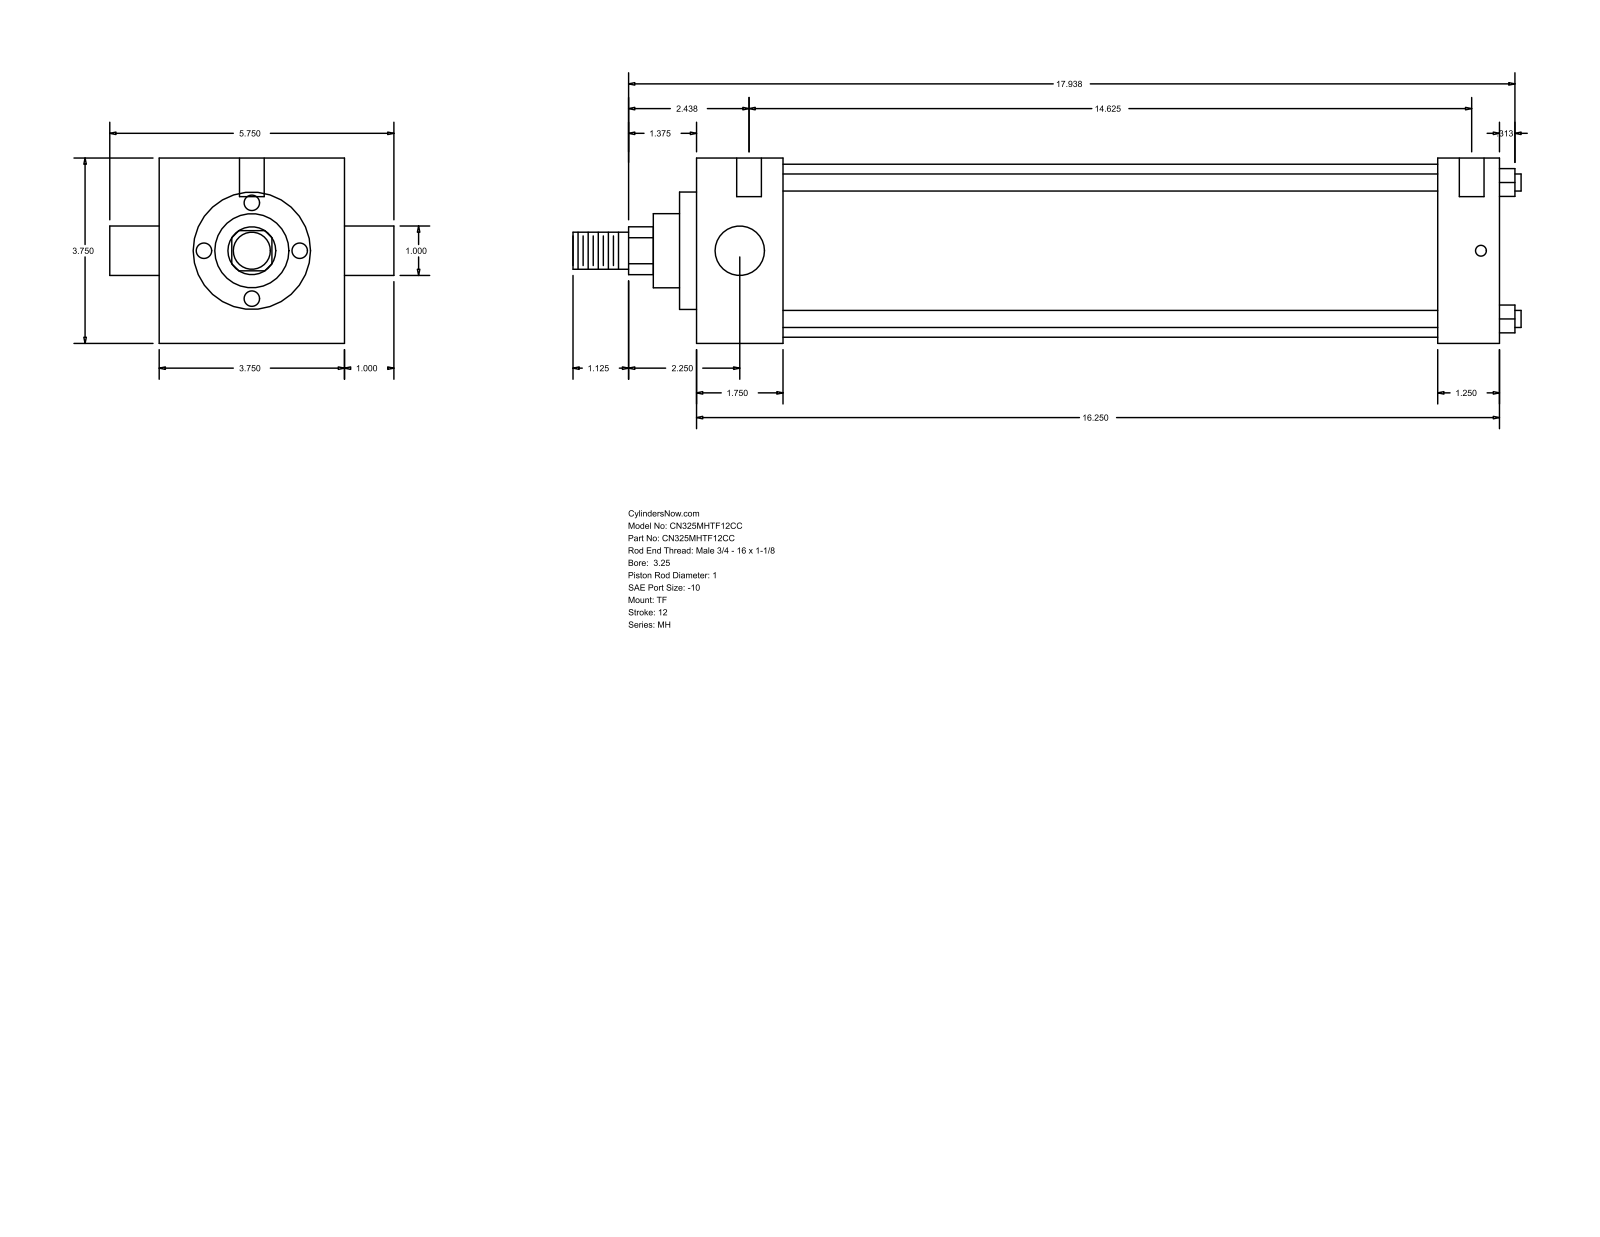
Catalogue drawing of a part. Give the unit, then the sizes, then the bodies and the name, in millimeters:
Units: millimetres
Overall size (bounding box): 487.36 × 146.05 × 95.25
Round holes (diameter × count): ⌀5.56 ×3, ⌀12.7 ×2
Round bosses / shafts (diameter × count): ⌀8.76 ×4, ⌀25.4 ×2, ⌀88.9 ×1, ⌀60.33 ×1, ⌀38.1 ×1, ⌀19.05 ×1
Partial cylindrical surfaces — rounded edges, fillets, slot ends (radius × count): R12.29 ×1
Main face-to-face distances: 95.24, 412.76, 44.46, 381.01, 336.55, 368.3, 31.75, 8.73, 53.19, 389.74
Hole centre spacings: 1.58, 4.76, 371.48, 373.06, 376.24, 377.82
Bodies: 0 solids, 86 faces (61 planar, 25 cylindrical, 0 other)
Part name (STEP PRODUCT): MH_TF__0325_1
STEP written by: GSSL Pune (CONFIG_CONTROL_DESIGN)
